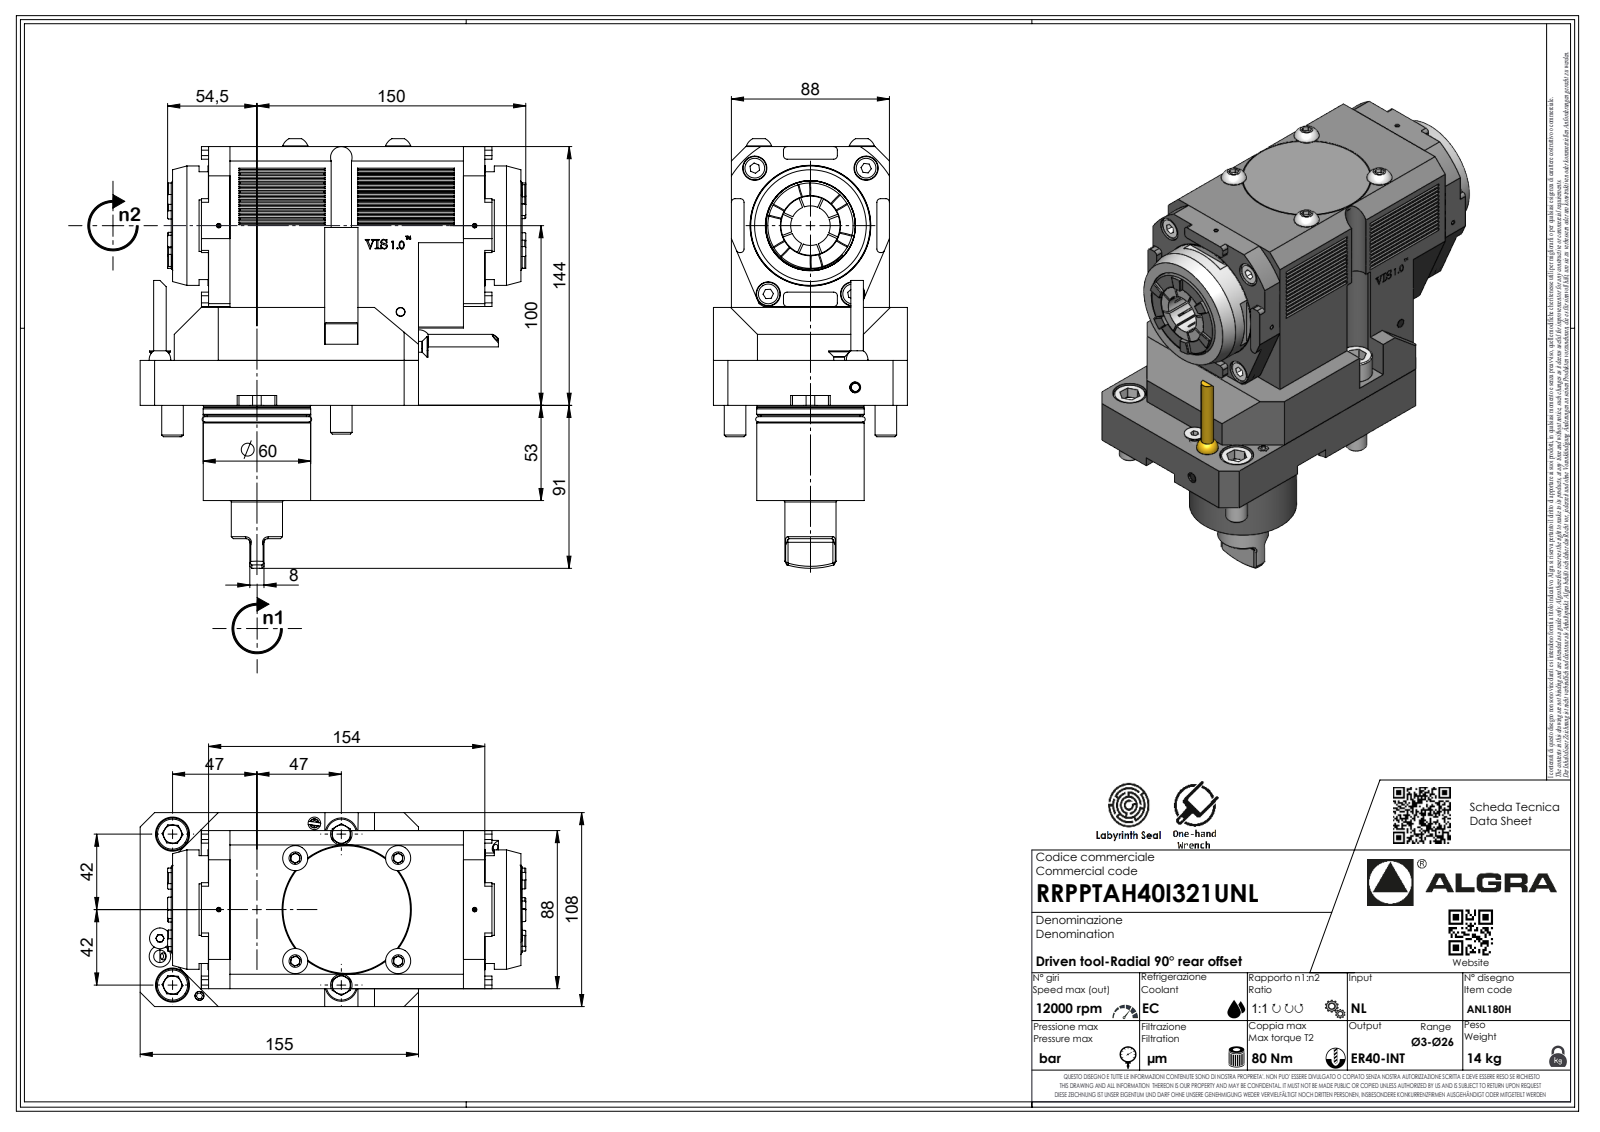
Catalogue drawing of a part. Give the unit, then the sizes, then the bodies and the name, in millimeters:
Units: millimetres
Overall size (bounding box): 239.1 × 212 × 108
Round holes (diameter × count): ⌀4 ×2, ⌀2.1 ×1
Round bosses / shafts (diameter × count): ⌀14 ×4, ⌀12 ×4, ⌀7 ×2, ⌀67 ×1, ⌀66.5 ×1, ⌀59.9 ×1, ⌀59.8 ×1, ⌀59.5 ×1
Partial cylindrical surfaces — rounded edges, fillets, slot ends (radius × count): R2 ×24, R0.33 ×7, R0.52 ×7, R3.7 ×7, R1 ×2, R0.21 ×1, R46 ×1, R52 ×1
Main face-to-face distances: 10, 98, 88, 144, 108, 20.1, 173.9, 137, 57, 194
Volume: 2 327 000 mm³ · Surface area: 137 000 mm²
Bodies: 1 solid, 530 faces (338 planar, 98 cylindrical, 94 other)
Part name (STEP PRODUCT): RRPPTAH40I321UNL
STEP written by: SolidWorks 2023 (AUTOMOTIVE_DESIGN)
